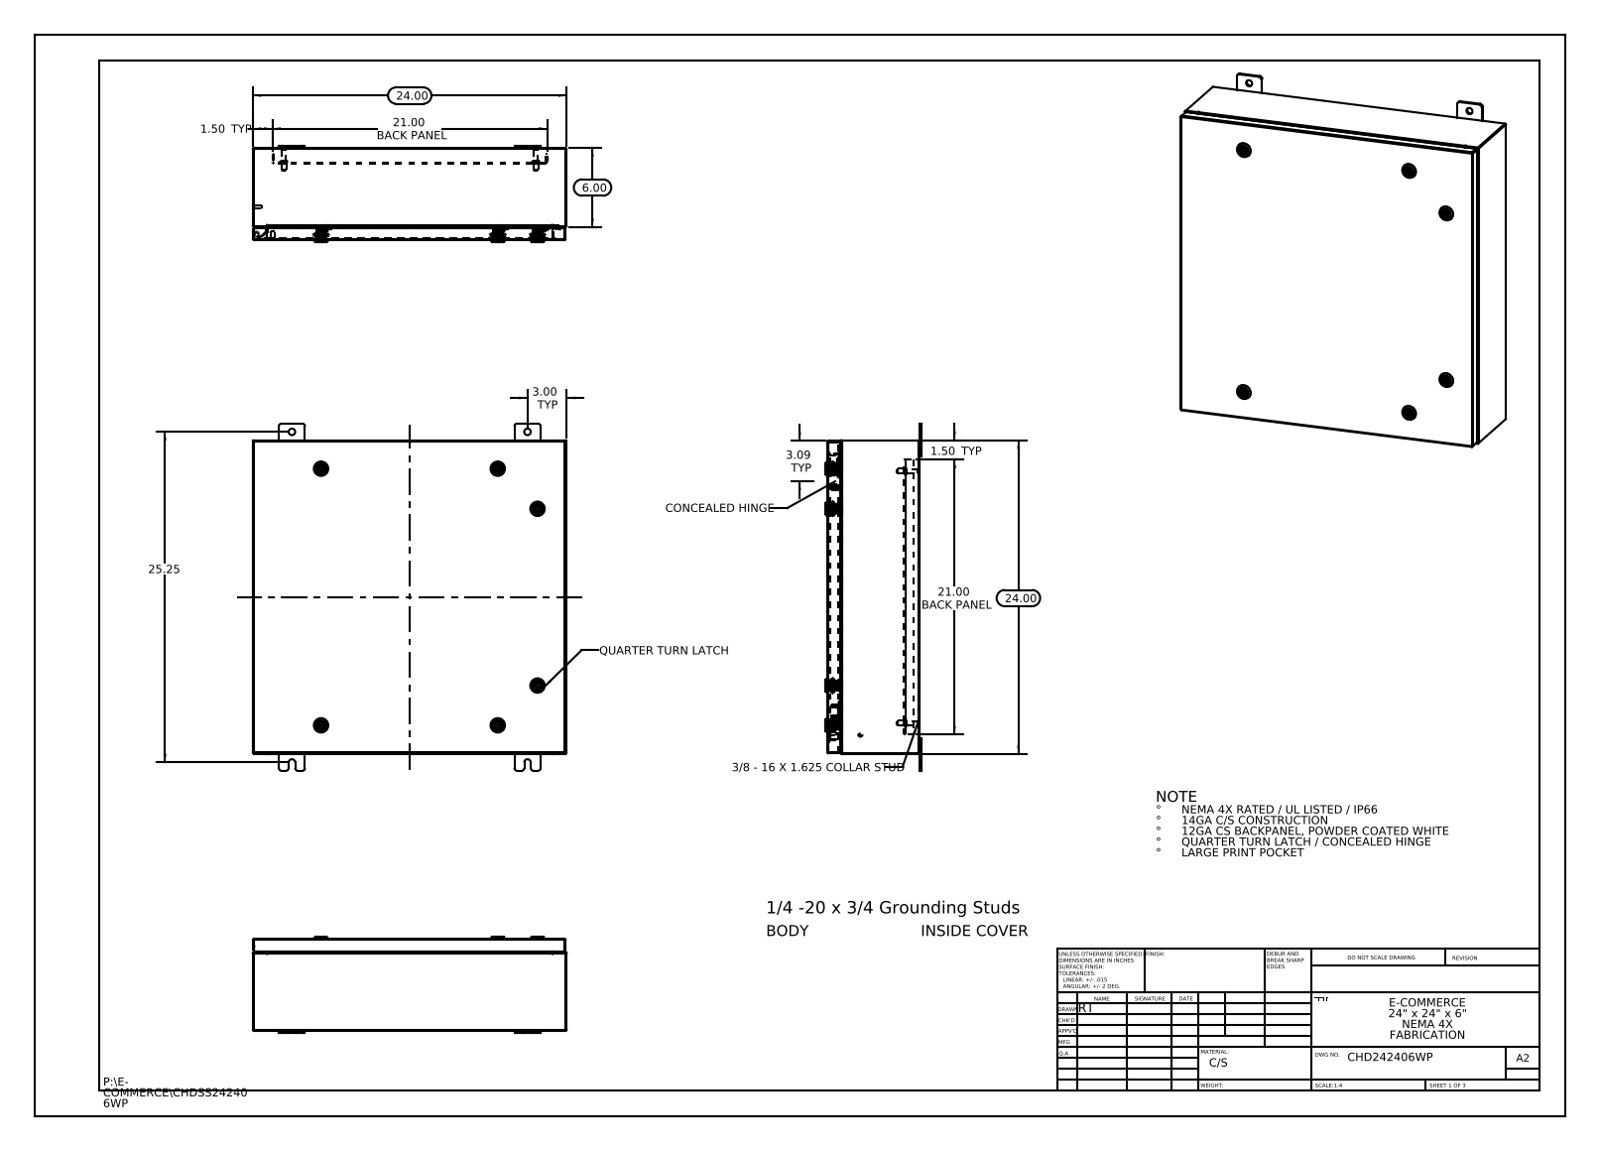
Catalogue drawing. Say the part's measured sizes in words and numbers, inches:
The part is named "Quarter-20 CD Stud; CHDSS242406WP Backpanel; CHDSS242406WP Cover; HW-CLH-E5-8004_Cam-232112-U-Industrilas (+8 more)". Its 3-D file was written by "SolidWorks 2013 (CONFIG_CONTROL_DESIGN)". It is 53 solids with 5376 faces: 1564 planar, 1676 cylindrical and 2136 other. Overall it measures 26.5 by 24 by 7.356 inches. Its volume is 204.2 cubic inches and its surface area 5 064 square inches. Round holes: 8 of diameter 0.5, 6 of diameter 0.197, 6 of diameter 0.394, 6 of diameter 0.4, 6 of diameter 0.63, 6 of diameter 0.787, 4 of diameter 0.136. Round bosses or shafts: 8 of diameter 0.236, 6 of diameter 1.102, 6 of diameter 0.78, 6 of diameter 0.626, 6 of diameter 0.61, 6 of diameter 0.531, 6 of diameter 0.392, 6 of diameter 0.114. Partial cylindrical surfaces (rounded edges, fillets, slot ends): 198 of radius 0.006, 198 of radius 0.118, 72 of radius 0.028, 24 of radius 0.02, 24 of radius 0.19, 24 of radius 0.197, 20 of radius 0.013, 18 of radius 0.088. The main face-to-face distances are 0.075, 0.074, 7.01, 6.935, 6.936, 6.861, 23.925, 0.104, 1, 1.075. The hole center spacings are 13.5, 1.858, 2.878, 3.065, 16.376, 16.815, 18, 19.25.
